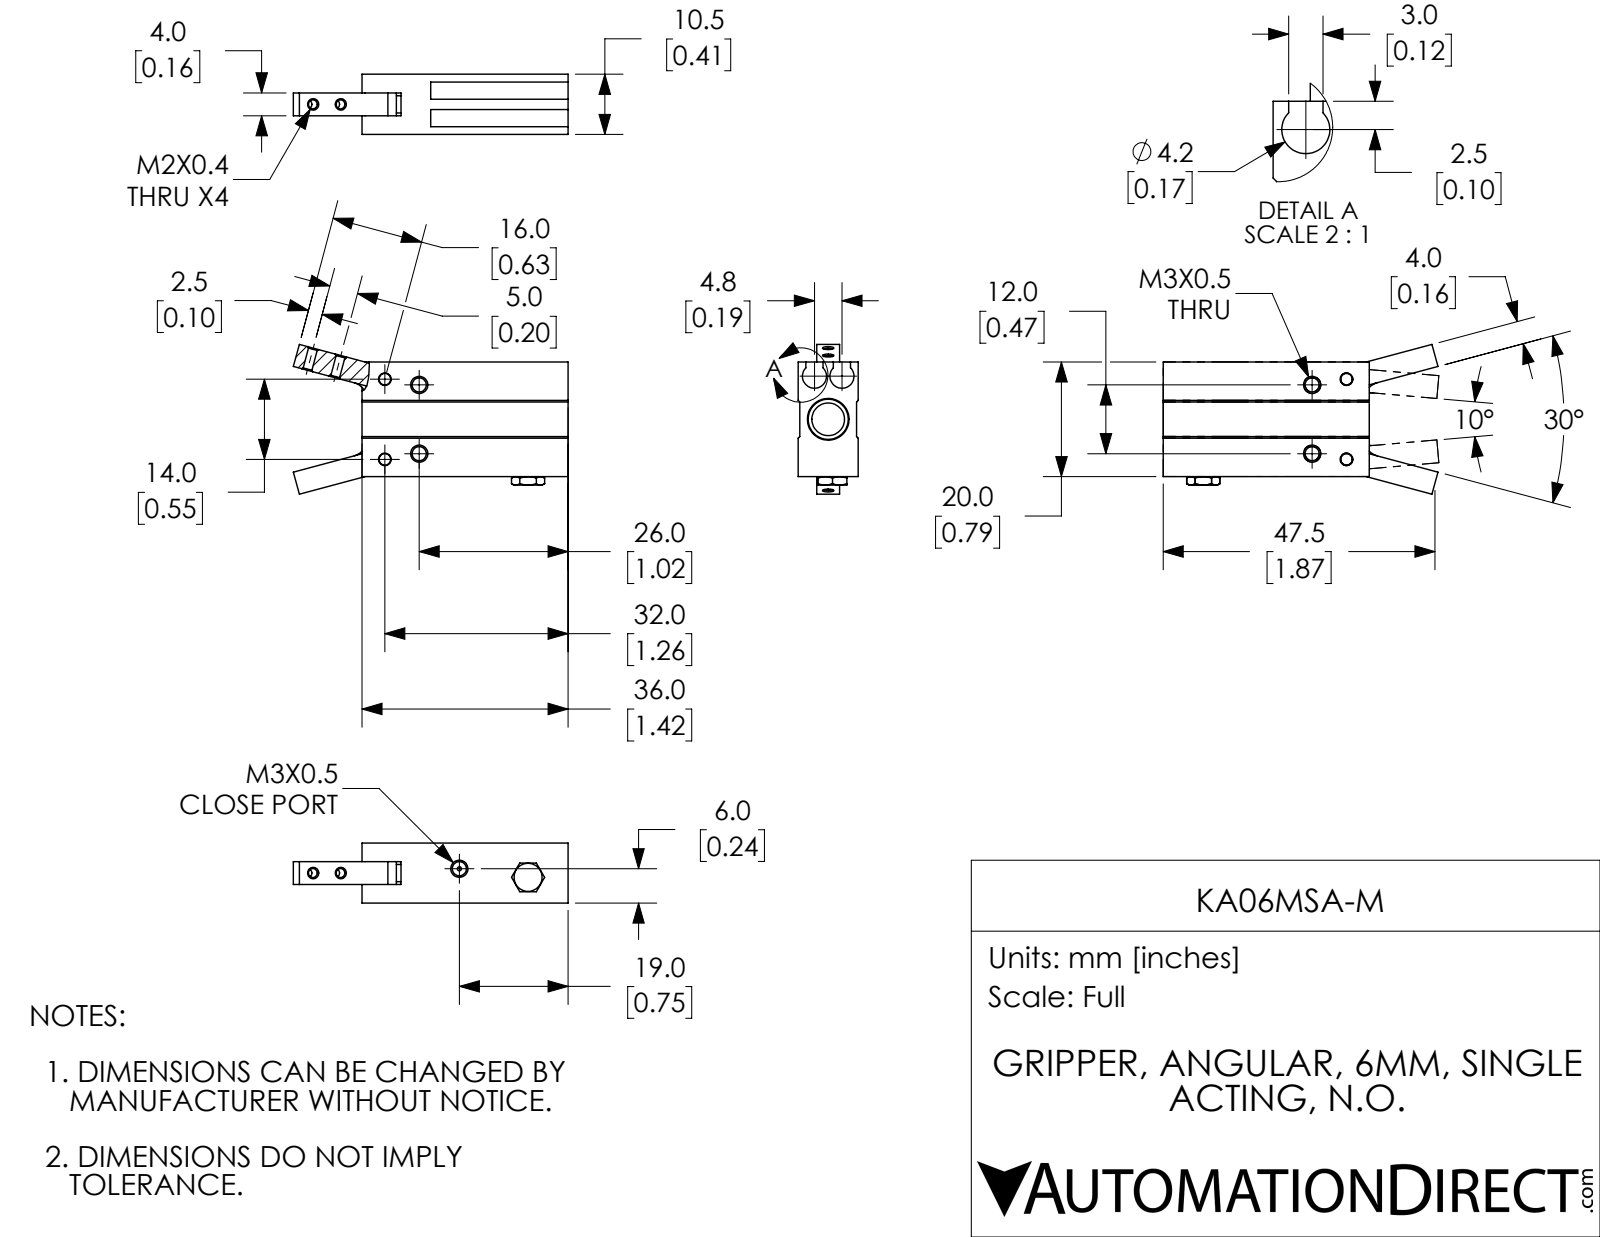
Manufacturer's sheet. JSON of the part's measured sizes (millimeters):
{"part_name": "KA06MSA-M; KA06MSA-M-4; KA06MSA-M-3; KA06MSA-M-2 (+1 more)", "step_written_by": "SolidWorks 2017 (AUTOMOTIVE_DESIGN)", "units": "millimeters", "bodies": {"solids": 4, "faces": 196, "planar": 74, "cylindrical": 67, "other": 55}, "overall_size": [47.97, 26.15, 10.5], "volume_mm3": 6380, "surface_area_mm2": 5343, "round_holes": [[2.46, 3], [1.57, 2], [1.57, 2], [2, 2], [1.5, 1], [2.46, 1], [3, 1], [5.7, 1], [6, 1], [7, 1], [8, 1]], "round_bosses_or_shafts": [[5.8, 1], [4, 1], [2.8, 1]], "partial_cylinders_radius": [[2, 2], [2.1, 2], [3, 2]], "face_to_face_distances": [10.5, 3.25, 7.25, 10.2, 2.95, 6.95, 4, 9.9, 20, 36], "hole_center_spacings": [5, 6.08, 7.25, 9.9, 14.32, 12, 12.09, 14]}
